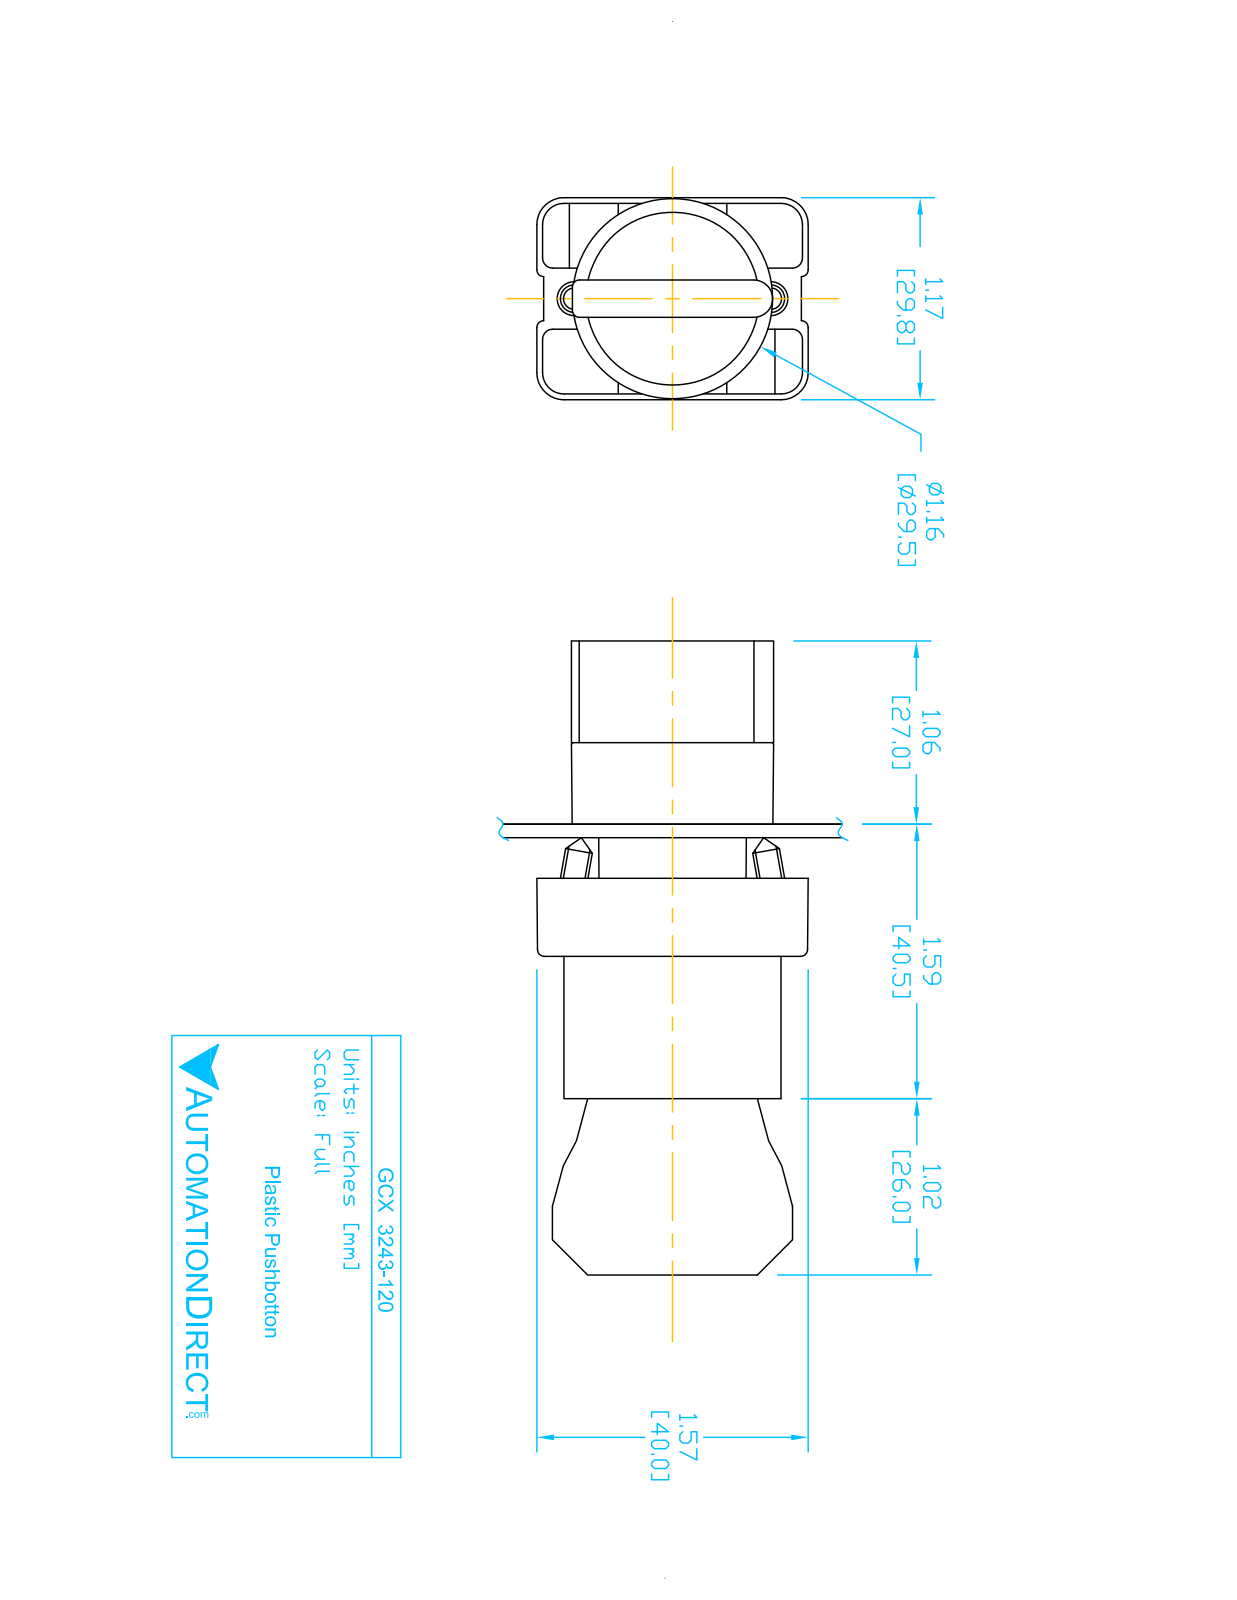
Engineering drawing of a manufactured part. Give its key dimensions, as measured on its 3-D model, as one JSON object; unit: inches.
{"part_name": "GCX3243-120; ECX3029-2; ECX1050; ecx1040 (+1 more)", "step_written_by": "SolidWorks 2016 (AUTOMOTIVE_DESIGN)", "units": "inches", "bodies": {"solids": 8, "faces": 445, "planar": 263, "cylindrical": 151, "other": 31}, "overall_size": [3.653, 1.581, 1.177], "volume_in3": 2.799, "surface_area_in2": 39, "round_holes": [[0.079, 2], [0.124, 2], [0.13, 2], [0.087, 1], [0.197, 1], [0.469, 1], [0.878, 1], [0.888, 1], [1.024, 1]], "round_bosses_or_shafts": [[0.157, 4], [1.175, 1], [1.004, 1], [0.945, 1], [0.856, 1], [0.78, 1], [0.504, 1]], "partial_cylinders_radius": [[0.059, 24], [0.041, 12], [0.124, 12], [0.157, 12], [0.039, 9], [0.128, 2], [0.02, 1], [0.063, 1]], "face_to_face_distances": [0.827, 2.02, 1.193, 0.579, 1.244, 1.171, 0.472, 0.469, 0.031, 0.033], "hole_center_spacings": [0.236, 0.544, 0.472, 0.49]}
